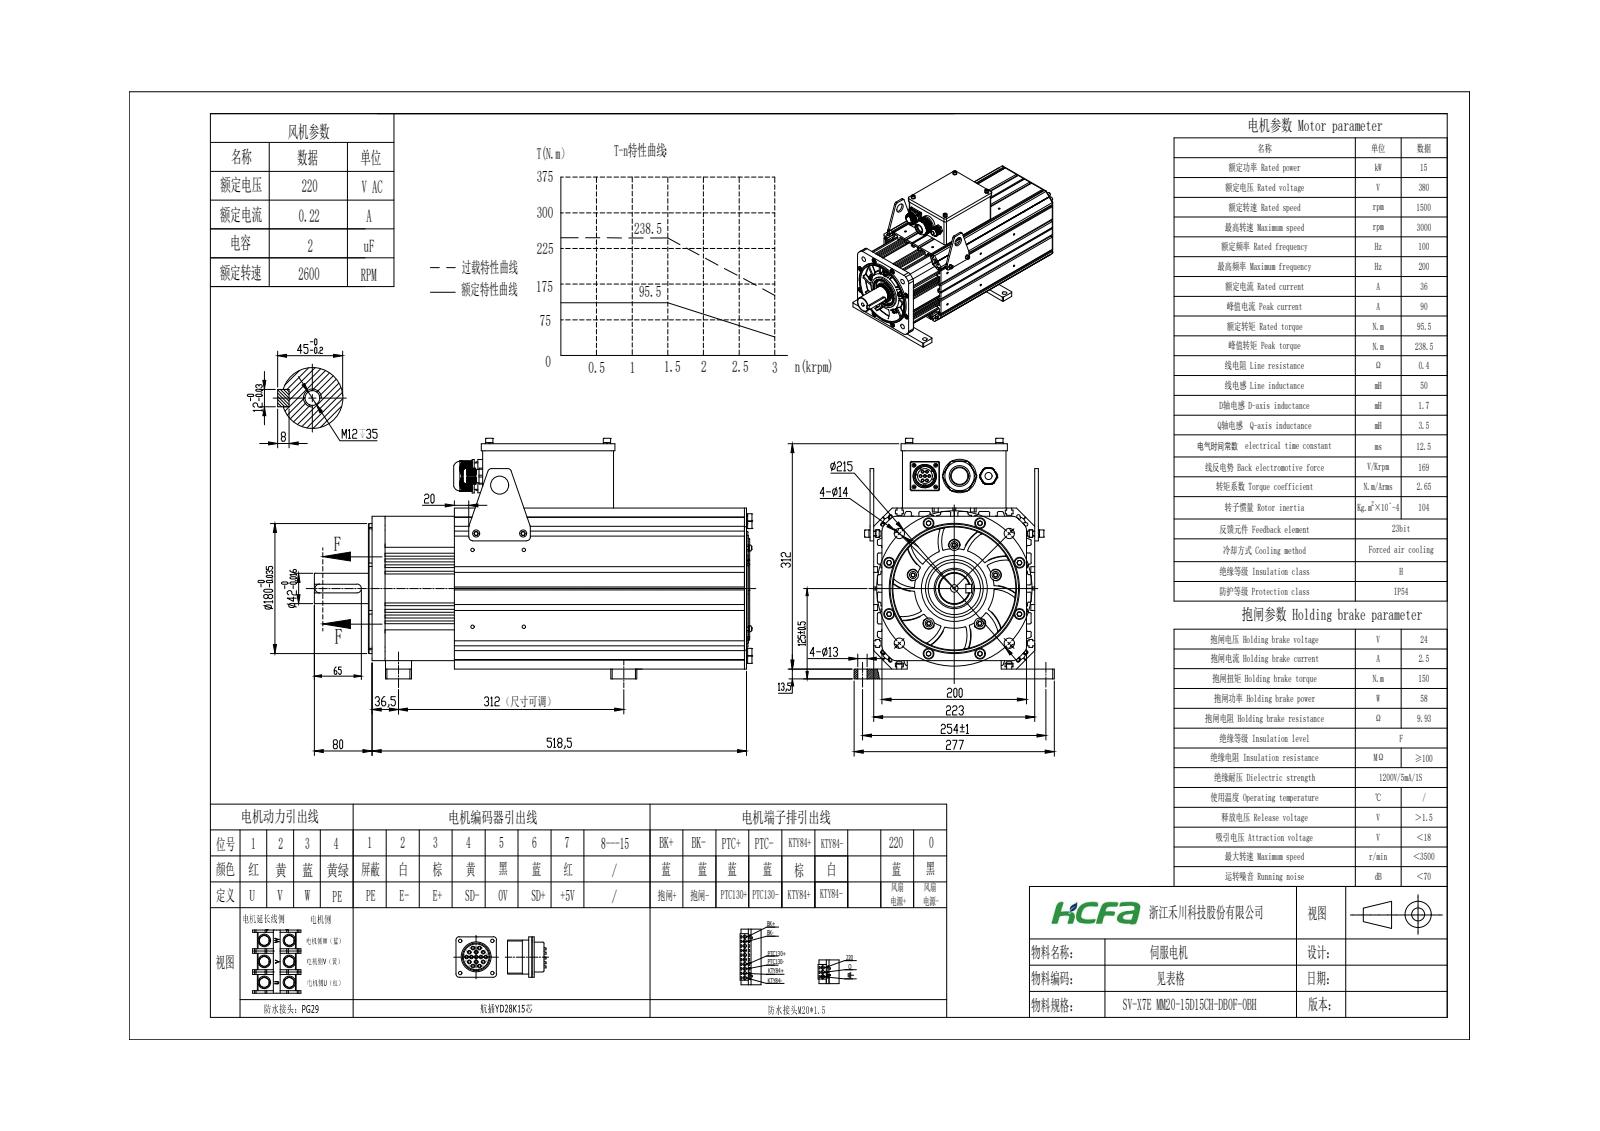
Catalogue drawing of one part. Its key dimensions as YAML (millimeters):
part_name: "15KW抱闸"
step_written_by: "SolidWorks 2021 (CONFIG_CONTROL_DESIGN)"
units: millimeters
bodies: {solids: 91, faces: 4316, planar: 2345, cylindrical: 1227, other: 744}
overall_size: [606.1, 333.1, 277]
volume: 6532000
surface_area: 2524000
round_holes:
  - {diameter: 5, count: 24}
  - {diameter: 6.8, count: 17}
  - {diameter: 6.68, count: 15}
  - {diameter: 9, count: 14}
  - {diameter: 6.5, count: 11}
  - {diameter: 15, count: 10}
  - {diameter: 3.5, count: 8}
  - {diameter: 8, count: 8}
  - {diameter: 4.2, count: 7}
  - {diameter: 4.5, count: 6}
  - {diameter: 14, count: 5}
  - {diameter: 2.5, count: 4}
round_bosses_or_shafts:
  - {diameter: 2, count: 24}
  - {diameter: 10, count: 17}
  - {diameter: 6, count: 17}
  - {diameter: 9.88, count: 15}
  - {diameter: 8, count: 14}
  - {diameter: 4, count: 11}
  - {diameter: 13, count: 10}
  - {diameter: 3, count: 8}
partial_cylinders:
  - {radius: 2, count: 84}
  - {radius: 0.5, count: 24}
  - {radius: 5, count: 20}
  - {radius: 3, count: 15}
  - {radius: 2.5, count: 14}
  - {radius: 10, count: 12}
  - {radius: 1.5, count: 8}
  - {radius: 2.41, count: 8}
face_to_face_distances: [223, 2.5, 5, 218, 6.5, 11.5, 211.5, 206.5, 8, 198.5]
hole_center_spacings: [112.5, 154.85, 106.4, 225, 1.77, 41.18, 42.89, 72.86]
